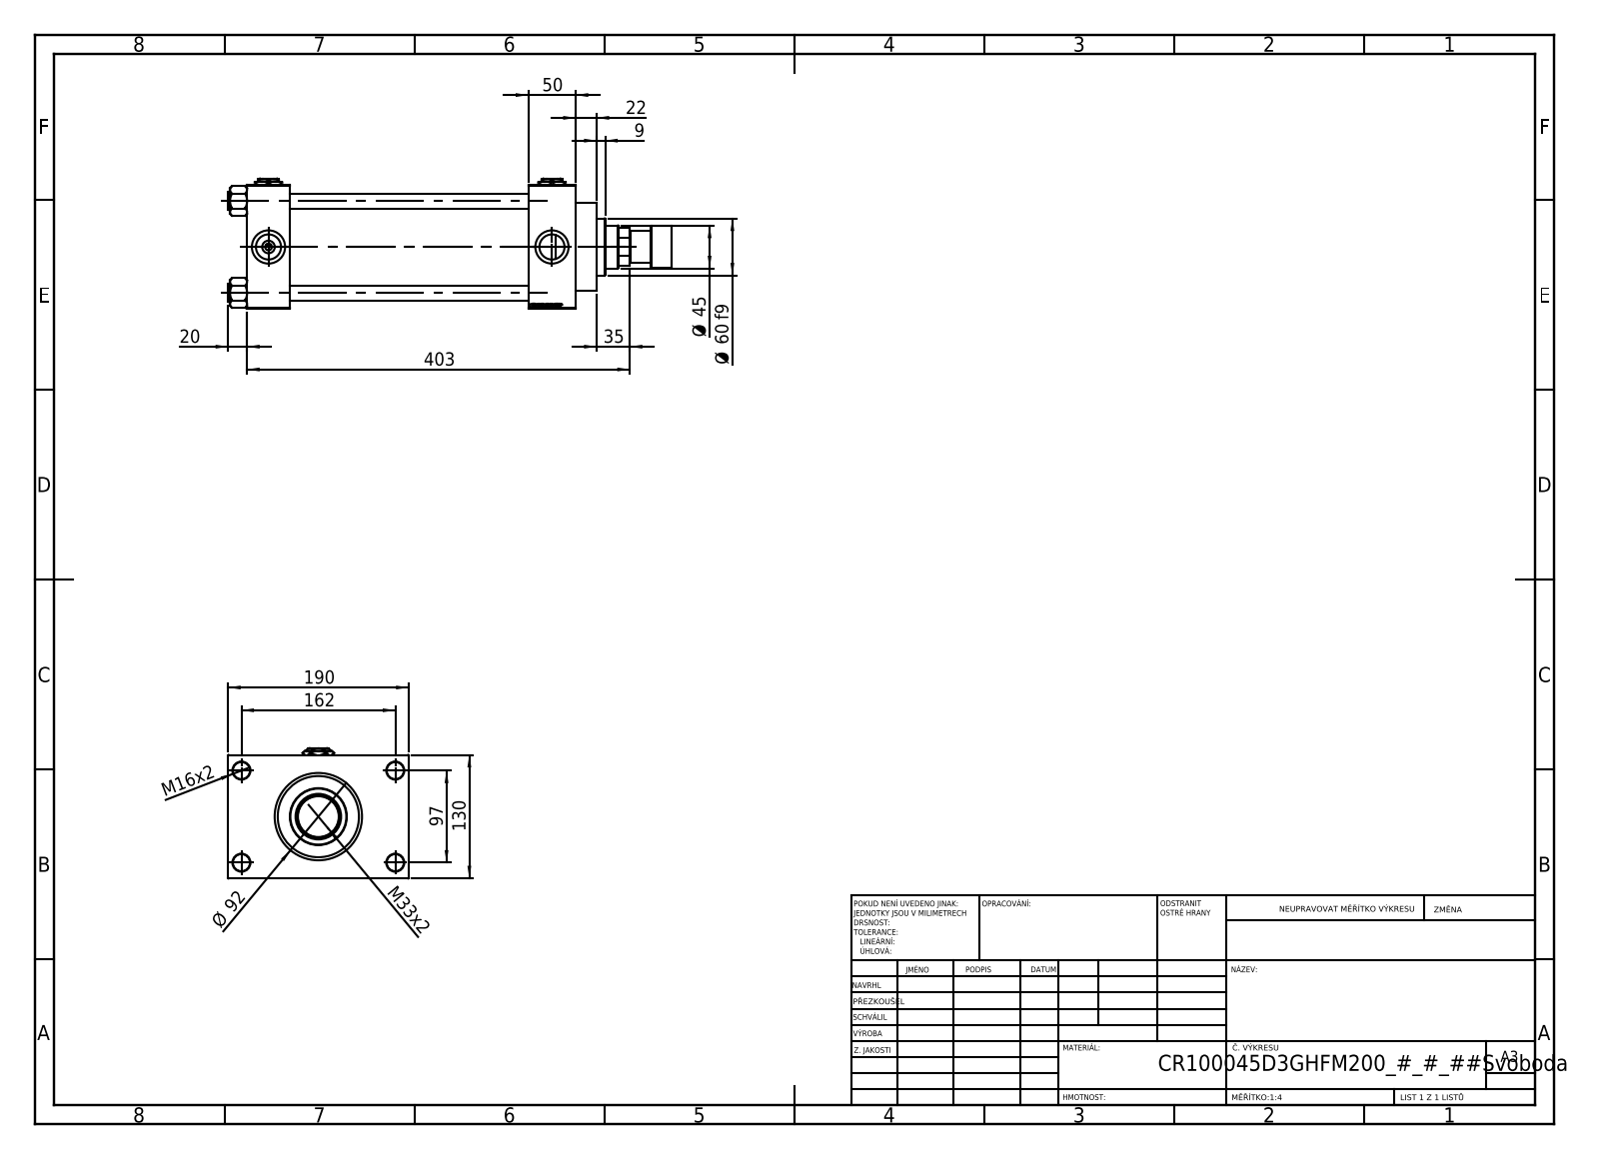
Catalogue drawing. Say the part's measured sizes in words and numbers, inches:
The part is named "V215_VC_A; NUT_M5_D; V215CR_ROD_END_F; Zatka_pro_OIL_PORT (+3 more)". Its 3-D file was written by "SolidWorks 2019 (CONFIG_CONTROL_DESIGN)". It is 14 solids with 1265 faces: 596 planar, 103 cylindrical and 566 other. Overall it measures 18.386 by 7.48 by 5.394 inches. Its volume is 197.4 cubic inches and its surface area 849.9 square inches. Round holes: 4 of diameter 0.63, 4 of diameter 0.709, 4 of diameter 1.041, 4 of diameter 1.378, 3 of diameter 0.276, 1 of diameter 1.24, 1 of diameter 1.772, 1 of diameter 1.89, 1 of diameter 2.992, 1 of diameter 3.366, 1 of diameter 3.937. Round bosses or shafts: 4 of diameter 0.748, 1 of diameter 4.173, 1 of diameter 3.622, 1 of diameter 2.362, 1 of diameter 1.732, 1 of diameter 1.299. The main face-to-face distances are 1.772, 5.118, 11.654, 9.882, 13.622, 11.85, 1.969, 1.181, 6.299, 3.78. The hole center spacings are 1.281, 2.698, 3.717, 3.815, 4.026, 5.096, 6.367, 3.819.
